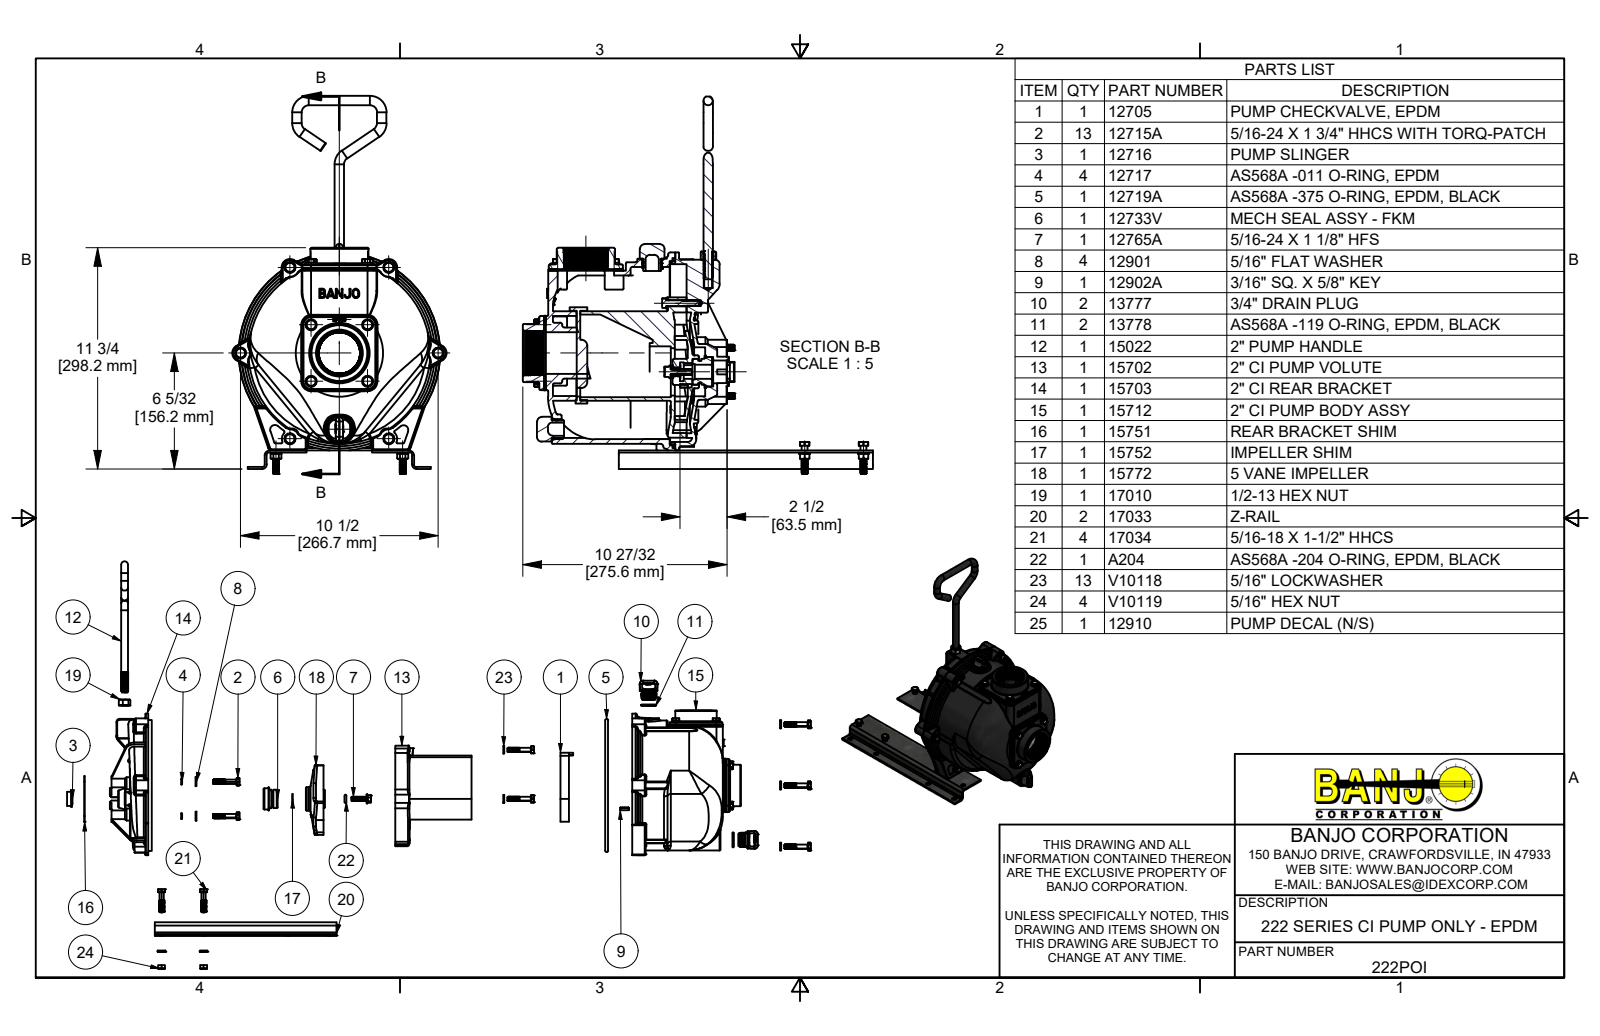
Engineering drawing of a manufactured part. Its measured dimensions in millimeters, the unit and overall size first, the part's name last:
Units: millimetres
Overall size (bounding box): 509.9 × 472.3 × 288.9
Round holes (diameter × count): ⌀8.2 ×21, ⌀8.7 ×18, ⌀6.8 ×9, ⌀6.4 ×8, ⌀8.7 ×8, ⌀9.5 ×8, ⌀8.2 ×7, ⌀6.4 ×4, ⌀10.8 ×4, ⌀20.7 ×4, ⌀6.4 ×2, ⌀12.7 ×2
Round bosses / shafts (diameter × count): ⌀7 ×260, ⌀6.8 ×164, ⌀8 ×25, ⌀14.8 ×21, ⌀25.4 ×8, ⌀12.7 ×5, ⌀17.5 ×4, ⌀78.6 ×2
Partial cylindrical surfaces — rounded edges, fillets, slot ends (radius × count): R3.2 ×119, R1.5 ×97, R3.5 ×26, R6.4 ×22, R12.7 ×21, R11.9 ×18, R7.2 ×17, R3.4 ×16
Main face-to-face distances: 2.7, 6.4, 22.2, 4.6, 2.4, 73.2, 19.6, 24.9, 0.4, 5.1
Hole centre spacings: 133.4, 231, 133.4, 27, 76.2, 82.5, 197.9, 309.6
Volume: 3 335 000 mm³ · Surface area: 1 219 000 mm²
Bodies: 84 solids, 7780 faces (1541 planar, 2776 cylindrical, 3463 other)
Part name (STEP PRODUCT): 222poi; 15712; 15712X; 17013 (+8 more)
STEP written by: Autodesk Inventor 2013 (AUTOMOTIVE_DESIGN)
